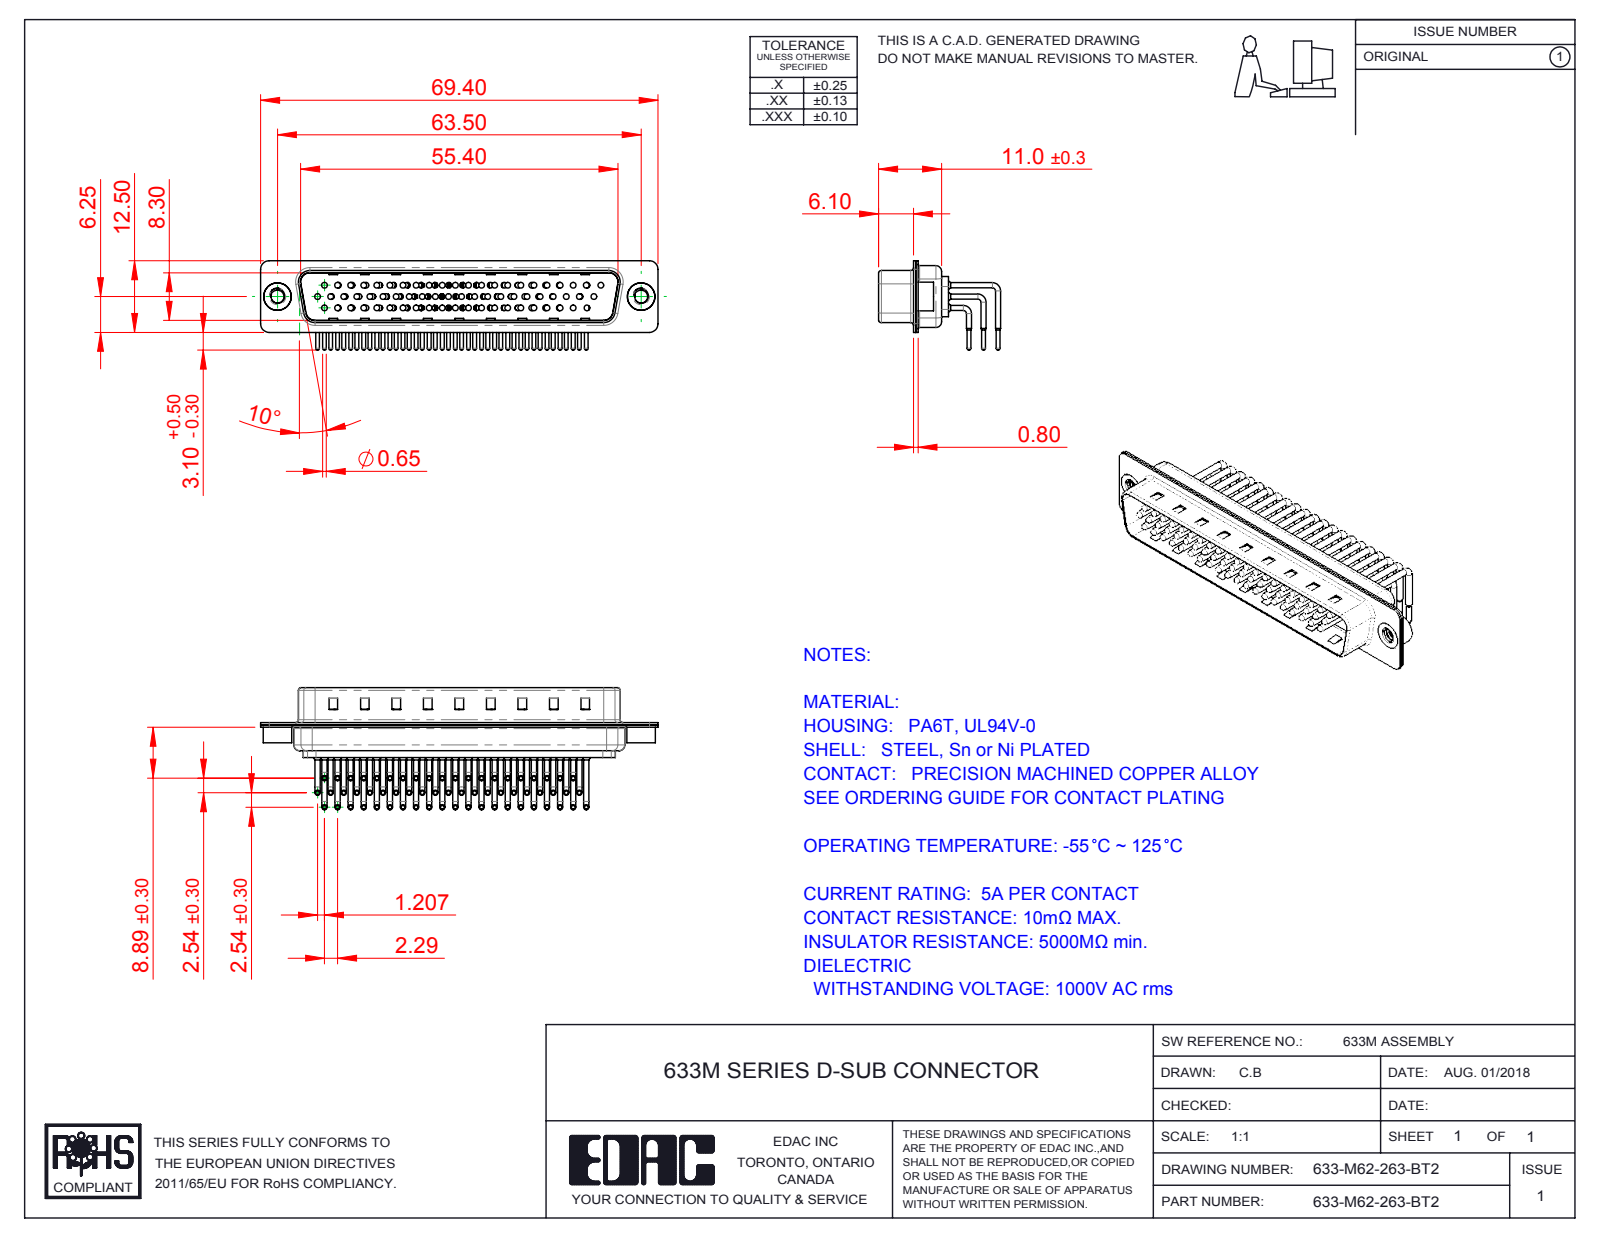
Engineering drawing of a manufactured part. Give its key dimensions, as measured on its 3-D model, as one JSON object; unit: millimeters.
{"part_name": "633M Shell Rear_62 Contacts; 633-M62-263-BT2; 633M Contact Row 2; 633M Shell Front_62 Contacts (+4 more)", "step_written_by": "SolidWorks 2016 (CONFIG_CONTROL_DESIGN)", "units": "millimeters", "bodies": {"solids": 67, "faces": 7232, "planar": 4171, "cylindrical": 2373, "other": 688}, "overall_size": [69.4, 21.32, 15.6], "volume_mm3": 4348, "surface_area_mm2": 13646, "round_holes": [[1, 62], [1.7, 62], [2, 62], [2.26, 2], [4, 2], [4.8, 2]], "round_bosses_or_shafts": [[0.9, 124], [1.5, 62], [0.65, 62], [1, 56], [5, 2], [4.9, 2]], "partial_cylinders_radius": [[1.01, 62], [1.5, 16], [2, 12], [0.5, 8], [1.6, 8], [0.25, 4], [0.6, 4], [0.65, 4]], "face_to_face_distances": [0.4, 0.85, 9.55, 8.7, 1.5, 1.9, 1.25, 10.4, 0.35, 0.45], "hole_center_spacings": [7.24, 2.32, 2.41, 4.13, 9.65, 4.83, 14.48, 11.04]}
